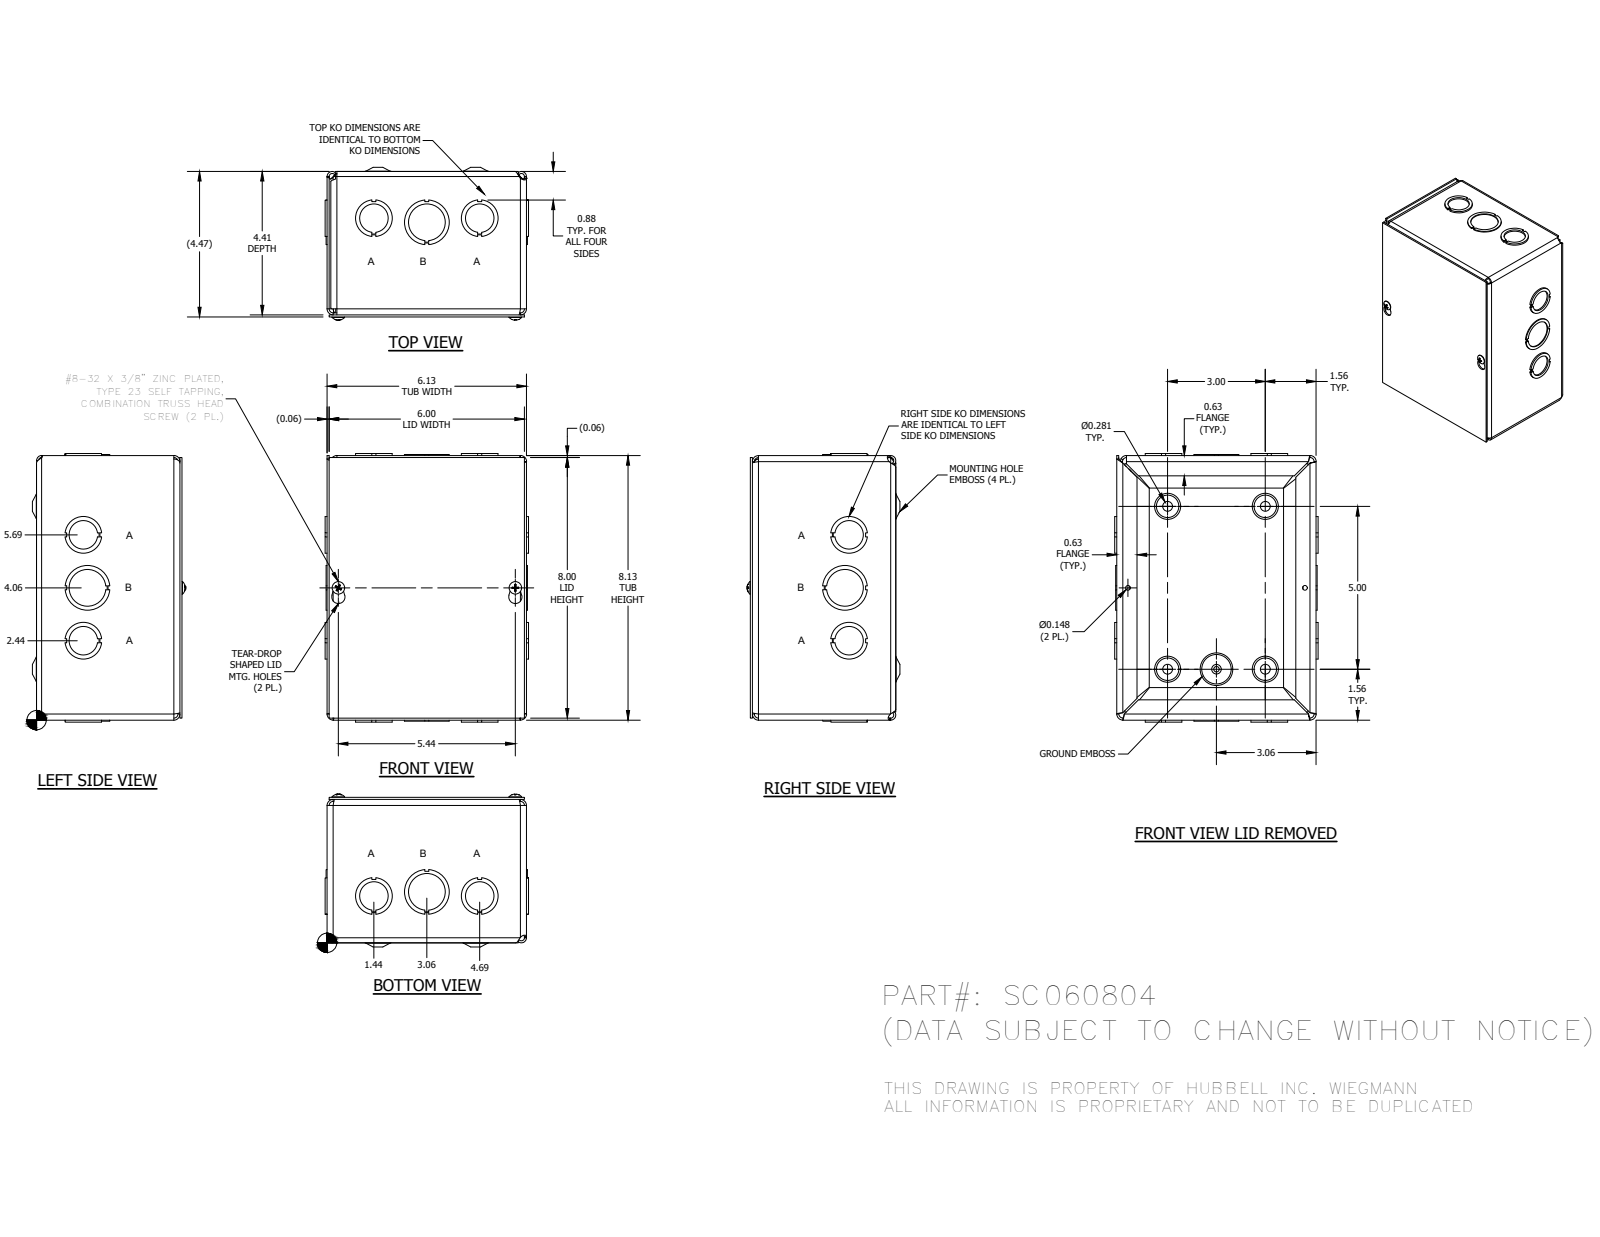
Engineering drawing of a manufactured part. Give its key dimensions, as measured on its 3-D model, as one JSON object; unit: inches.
{"part_name": "SC0608BKP; SC060804WRA; SC0608LID; 34056 (+1 more)", "step_written_by": "Autodesk Inventor 2014 (AUTOMOTIVE_DESIGN)", "units": "inches", "bodies": {"solids": 20, "faces": 630, "planar": 373, "cylindrical": 129, "other": 128}, "overall_size": [8.249, 6.249, 4.693], "round_holes": [[1.125, 6], [0.3, 4], [0.875, 4], [0.148, 2], [1.375, 2], [0.165, 1]], "round_bosses_or_shafts": [[0.384, 2], [0.164, 2], [0.228, 1]], "partial_cylinders_radius": [[0.125, 10], [0.187, 8], [0.055, 4], [0.062, 4], [0.094, 4], [0.117, 4], [0.124, 4], [0.156, 4]], "face_to_face_distances": [0.062, 4.343, 6.063, 4.405, 0.063, 4.406, 4.468, 0.062, 6.125, 6.001], "hole_center_spacings": [1.5, 1.63, 1.63, 2.781, 2.781, 3, 3.25, 4.904]}
